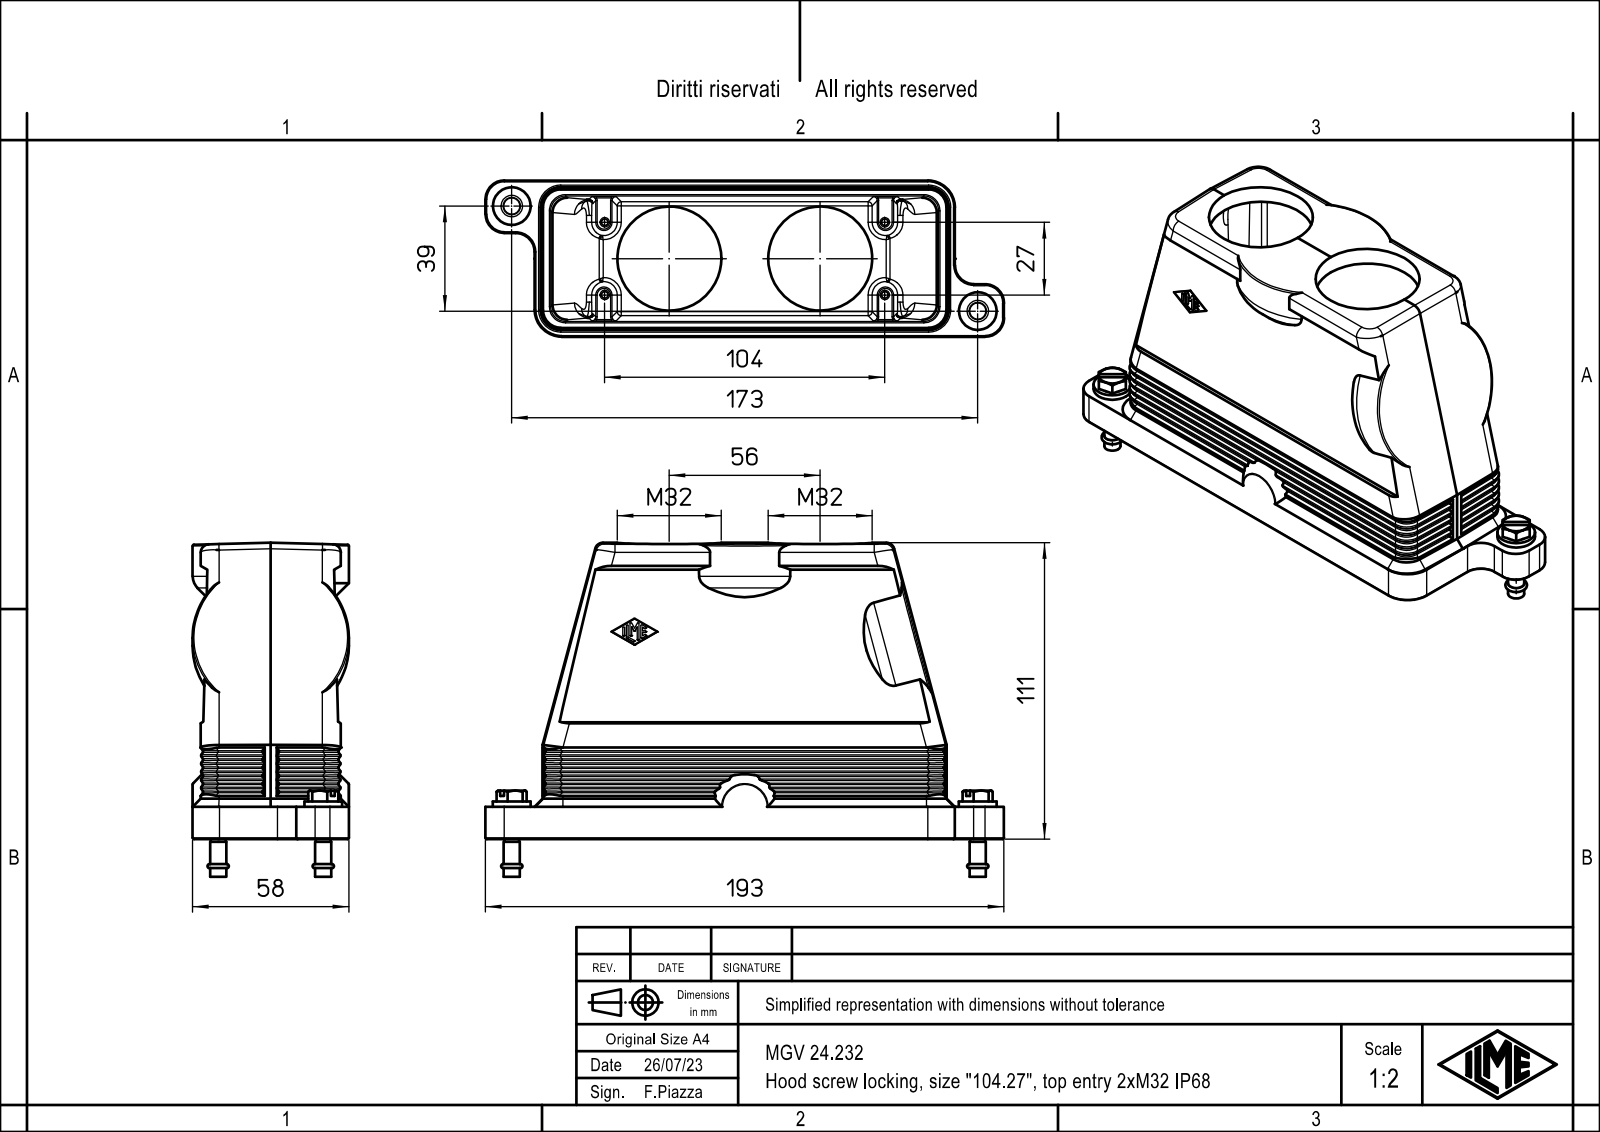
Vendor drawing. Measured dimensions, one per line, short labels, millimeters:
name: MGV 24.232
written by: Creo Elements/Direct Modeling 20.1B 02-Apr-2019 (C) Parametric Technology GmbH (AUTOMOTIVE_DESIGN)
unit: mm
bodies: 1 solid, 730 faces (246 planar, 189 cylindrical, 295 other)
size: 192.5 × 124 × 58
volume: 175 020 mm³; area: 97 403 mm²
holes: 4× ⌀3.5, 2× ⌀6.5, 2× ⌀14, 2× ⌀38.6
bosses: 2× ⌀6, 2× ⌀5.5
rounds: 62× R7, 21× R0.33, 14× R0.5, 14× R1.5, 8× R5.5, 6× R3, 4× R7.3, 3× R0.18
face distances: 3, 55, 3.33, 22.53, 127.03, 104.5, 58, 1.67, 1.66, 41.6
hole spacings: 27.54, 81.13, 27, 35.02, 47.74, 61.66, 104, 107.45
